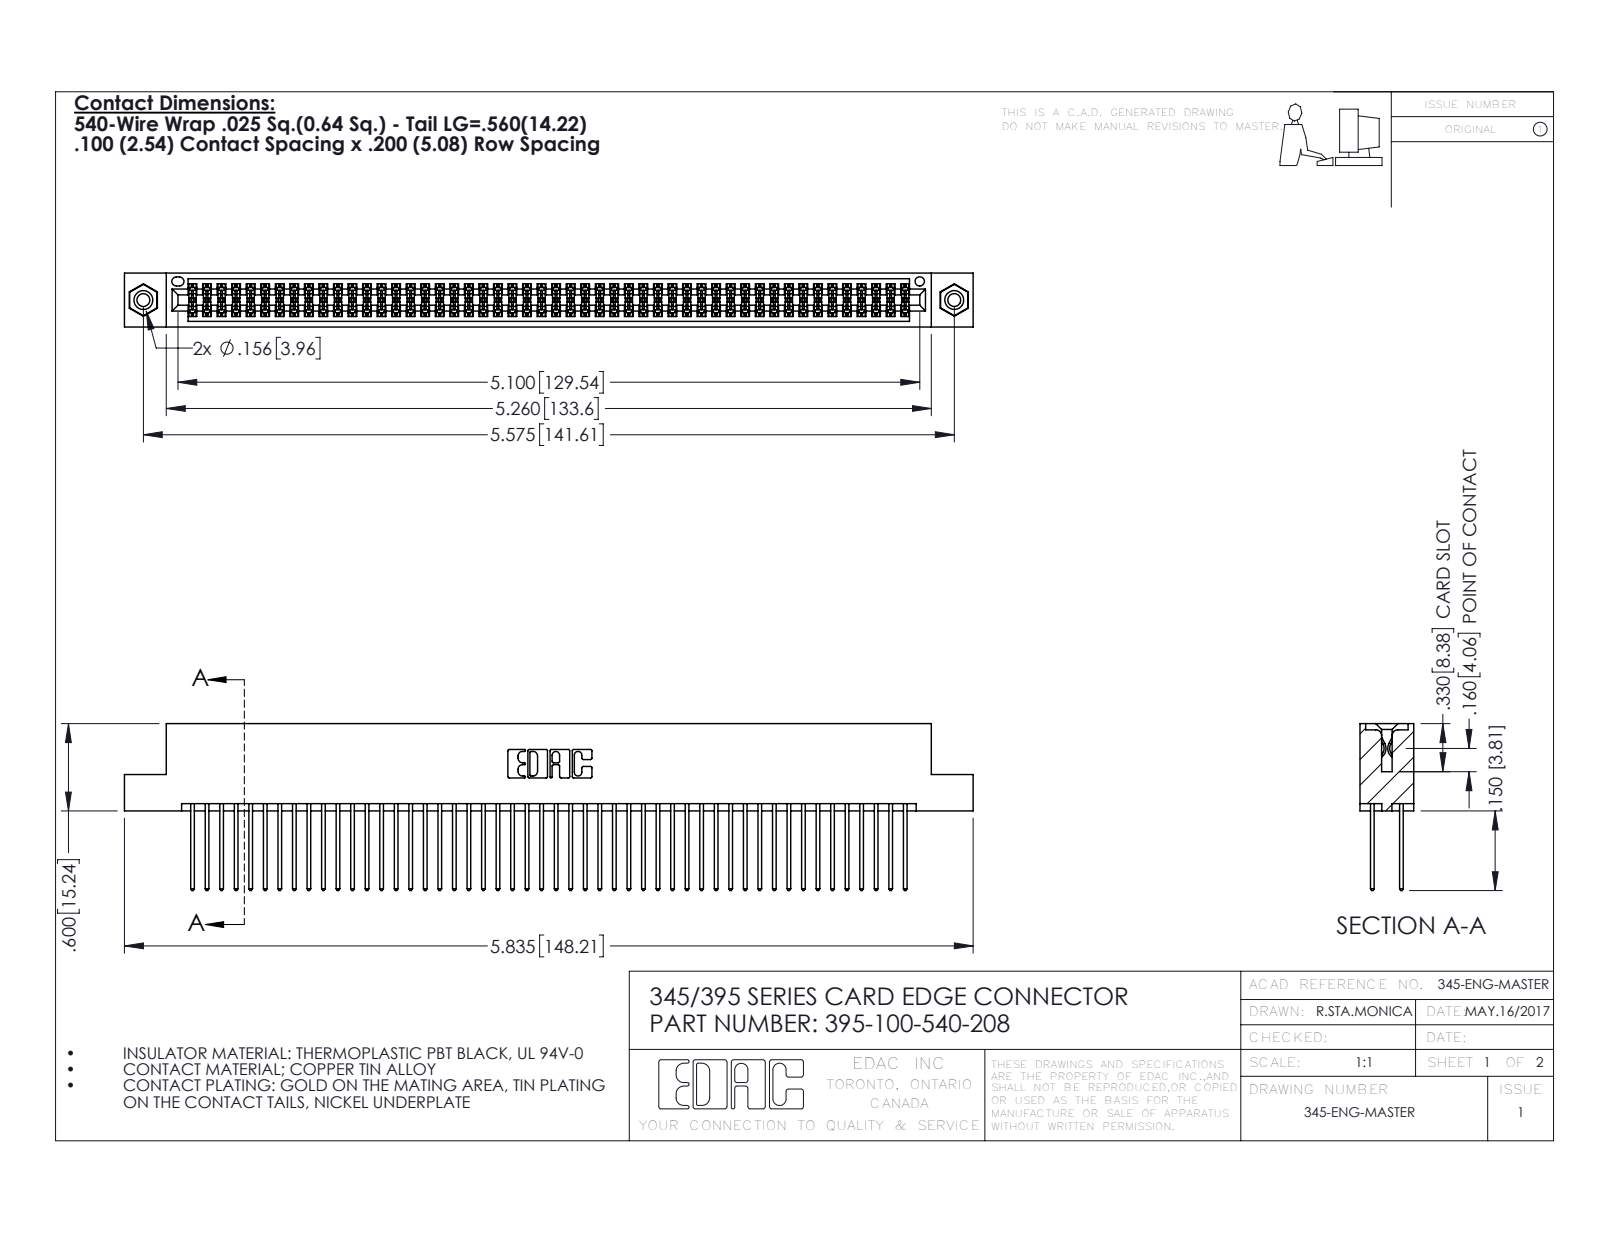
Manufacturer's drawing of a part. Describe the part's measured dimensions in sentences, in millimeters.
The part is named "345-292-001_345-293-140; 345 Part_Flush Mounting Lugs - 0.156 Dia-TI; 345-250-001_345-250-003-102; 395-100-540-208". Its 3-D file was written by "SolidWorks 2016 (CONFIG_CONTROL_DESIGN)". It is 103 solids with 5186 faces: 3412 planar, 1758 cylindrical and 16 other. Overall it measures 148.2 by 29.1 by 9.4 millimeters. Its volume is 14 800 cubic millimeters and its surface area 23 870 square millimeters. Round holes: 2 of diameter 2.3, 2 of diameter 3.2, 2 of diameter 4, 1 of diameter 1.6. Round bosses or shafts: 2 of diameter 3.9. Partial cylindrical surfaces (rounded edges, fillets, slot ends): 150 of radius 0.2, 100 of radius 0.3, 22 of radius 0.3, 6 of radius 0.2, 6 of radius 0.8, 3 of radius 0.7, 2 of radius 0.4, 2 of radius 0.5. The main face-to-face distances are 1.8, 7.6, 5.1, 2.5, 6.9, 0.6, 9.4, 5.7, 4.4, 3.8. The hole center spacings are 6.9, 135.6, 141.6.
